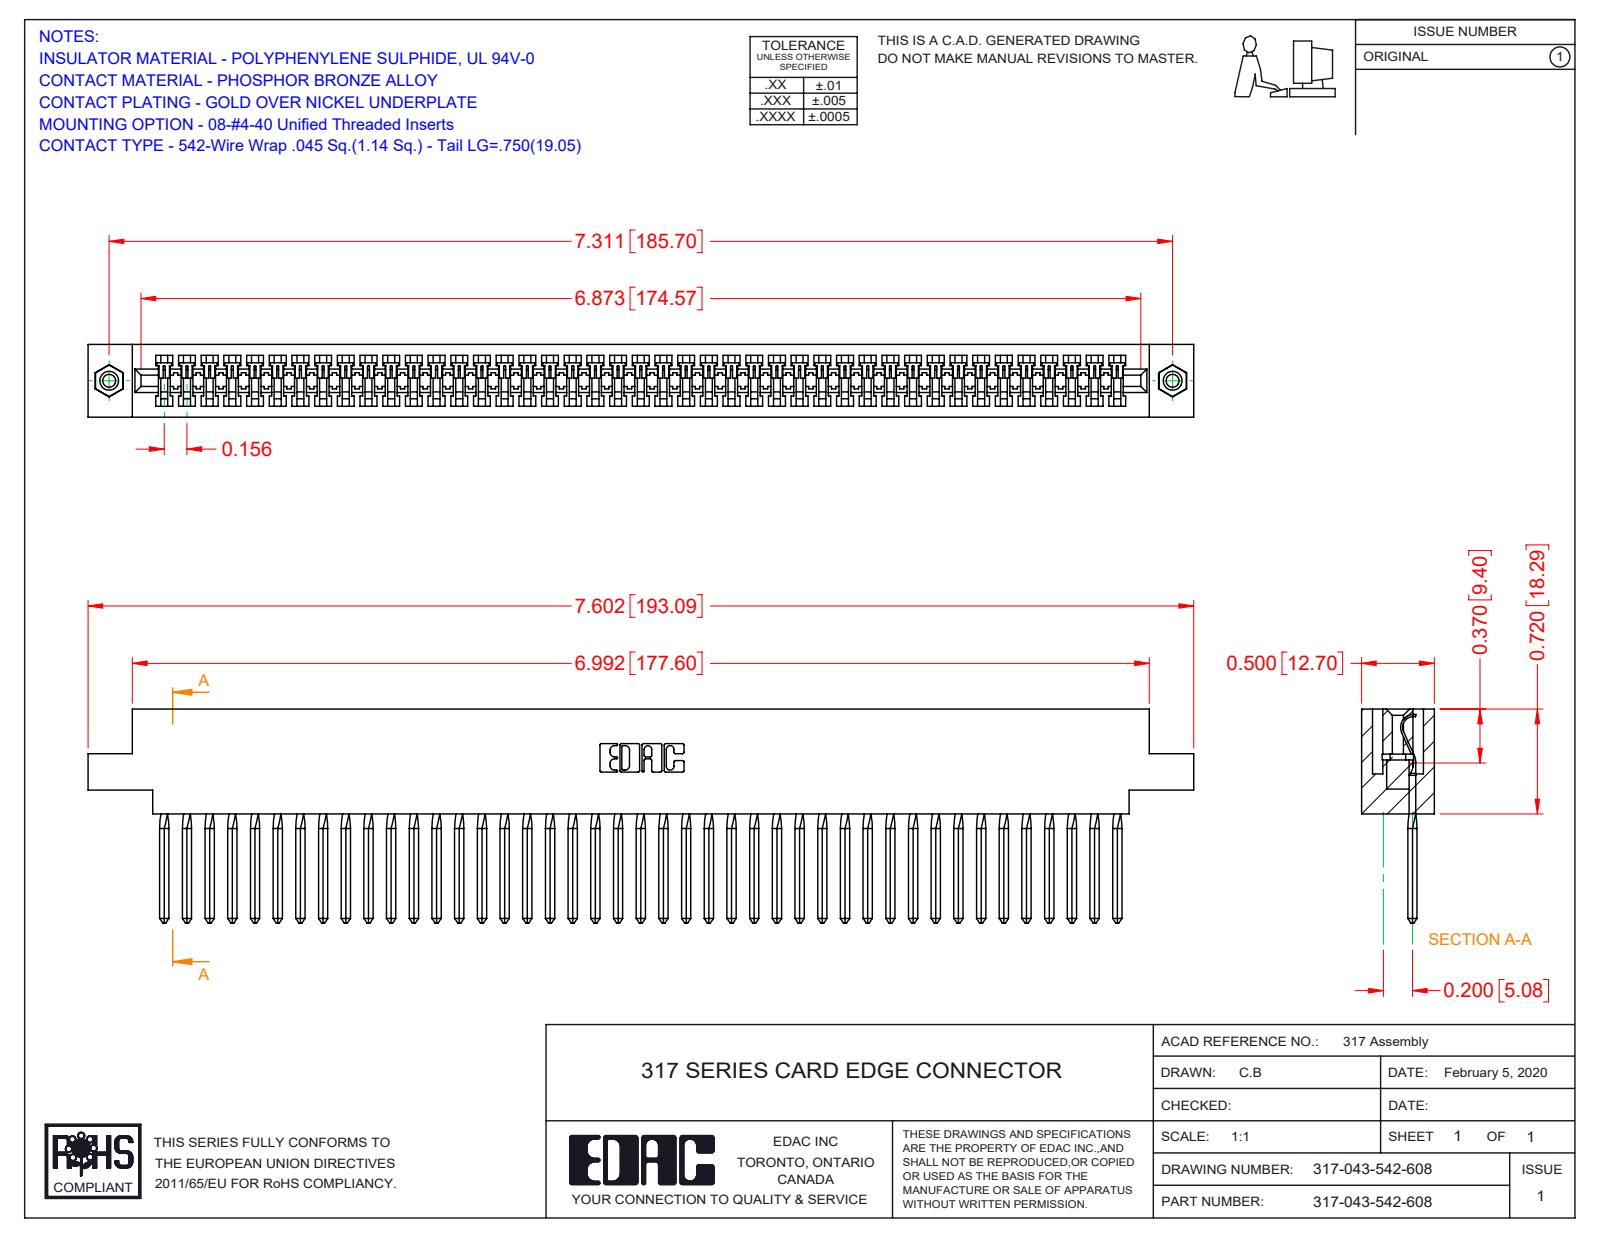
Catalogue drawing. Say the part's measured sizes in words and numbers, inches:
The part is named "345-250-001_345-250-003-102; 317-290-003_542; 317 Part_.156 Dia - TI; 317-043-542-608". Its 3-D file was written by "SolidWorks 2016 (CONFIG_CONTROL_DESIGN)". It is 46 solids with 3387 faces: 2842 planar, 357 cylindrical and 188 other. Overall it measures 7.602 by 1.47 by 0.5 inches. Its volume is 1.821 cubic inches and its surface area 56.51 square inches. Round holes: 2 of diameter 0.089, 2 of diameter 0.125, 2 of diameter 0.156. Round bosses or shafts: 2 of diameter 0.155. Partial cylindrical surfaces (rounded edges, fillets, slot ends): 86 of radius 0.006, 22 of radius 0.01, 6 of radius 0.007, 6 of radius 0.031, 3 of radius 0.026, 1 of radius 0.074, 1 of radius 0.089, 1 of radius 0.1. The main face-to-face distances are 0.5, 0.075, 0.425, 0.35, 0.72, 0.136, 0.195, 0.211, 0.289, 0.213. The hole center spacings are 7.311.
